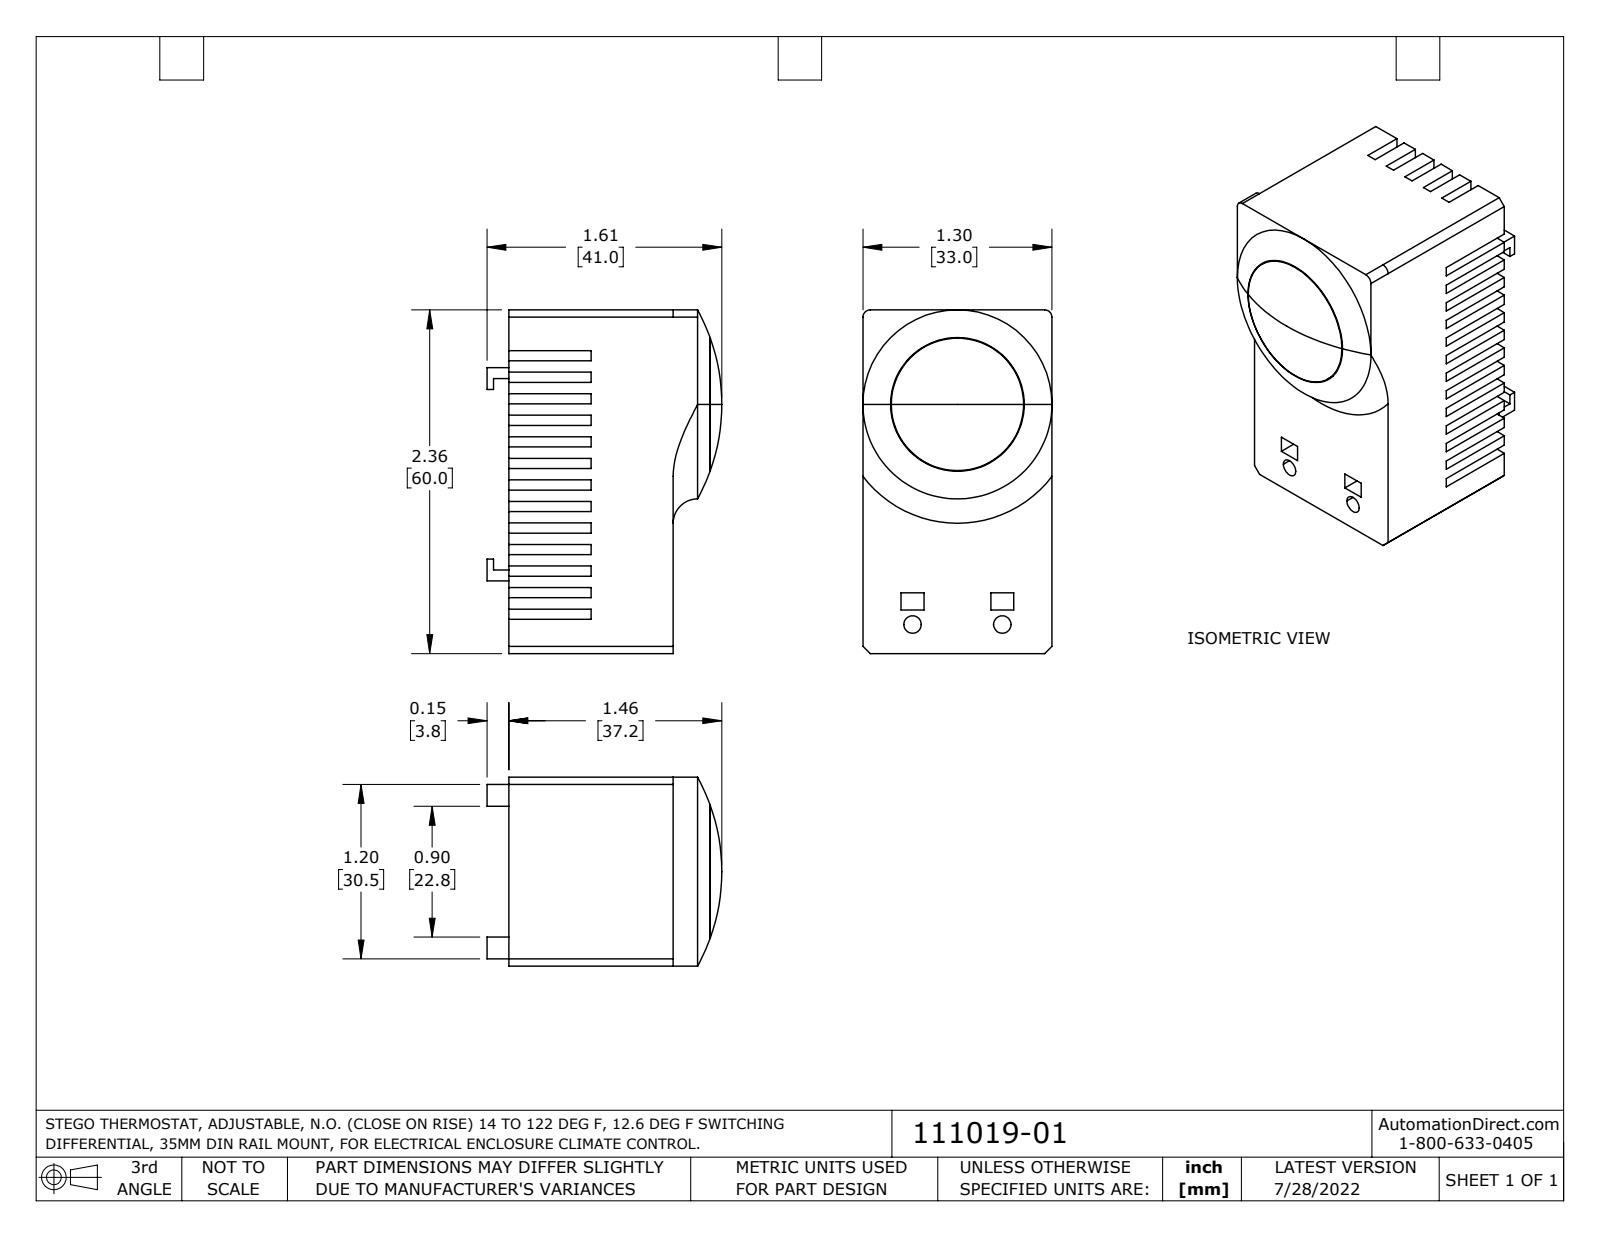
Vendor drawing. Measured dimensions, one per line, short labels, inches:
name: 111019-01_Default
written by: SolidWorks 2021 (CONFIG_CONTROL_DESIGN)
unit: in
bodies: 1 solid, 198 faces (183 planar, 10 cylindrical, 5 other)
size: 2.362 × 1.614 × 1.299
volume: 3.737 in³; area: 19.92 in²
holes: 2× ⌀0.12, 1× ⌀0.919
bosses: 1× ⌀0.909
rounds: 2× R0.05
face distances: 1.299, 0.148, 0.07, 2.362, 0.296, 1.13, 0.444, 0.592, 0.078, 0.218
hole spacings: 1.544, 0.617
